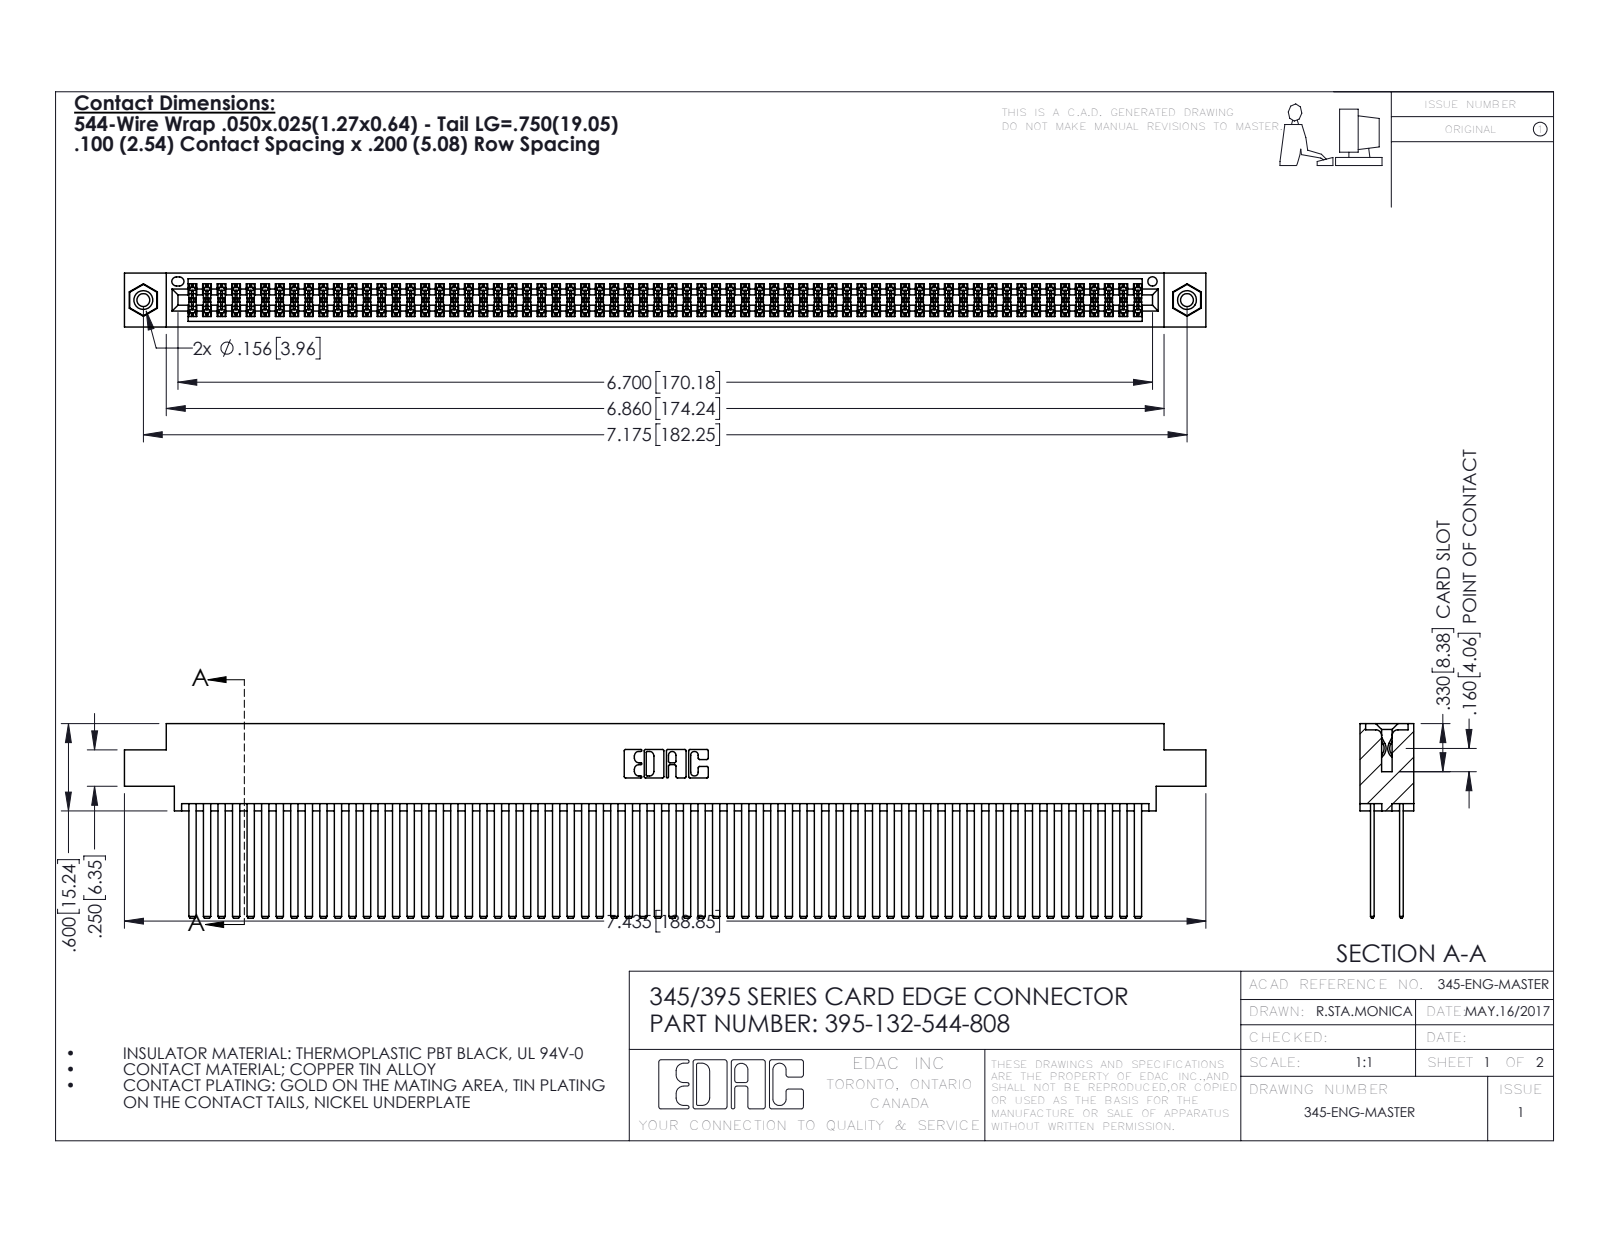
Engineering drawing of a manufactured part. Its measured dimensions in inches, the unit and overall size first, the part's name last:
Units: inches
Overall size (bounding box): 7.435 × 1.337 × 0.37
Round holes (diameter × count): ⌀0.089 ×2, ⌀0.125 ×2, ⌀0.156 ×2, ⌀0.064 ×1
Round bosses / shafts (diameter × count): ⌀0.155 ×2
Partial cylindrical surfaces — rounded edges, fillets, slot ends (radius × count): R0.006 ×198, R0.01 ×22, R0.007 ×6, R0.031 ×6, R0.026 ×3, R0.014 ×2, R0.019 ×2, R0.022 ×2
Main face-to-face distances: 0.2, 0.025, 0.072, 0.098, 0.272, 0.298, 0.225, 0.175, 0.37, 0.15
Hole centre spacings: 0.27, 6.939, 7.175
Volume: 1.239 in³ · Surface area: 55.88 in²
Bodies: 135 solids, 5998 faces (3944 planar, 2038 cylindrical, 16 other)
Part name (STEP PRODUCT): 395-132-544-808; 345 Part_0.170 Offset - 0.156 Dia-TI; 345-250-001_345-250-003-102; 345-292-001_345-293-144
STEP written by: SolidWorks 2016 (CONFIG_CONTROL_DESIGN)
